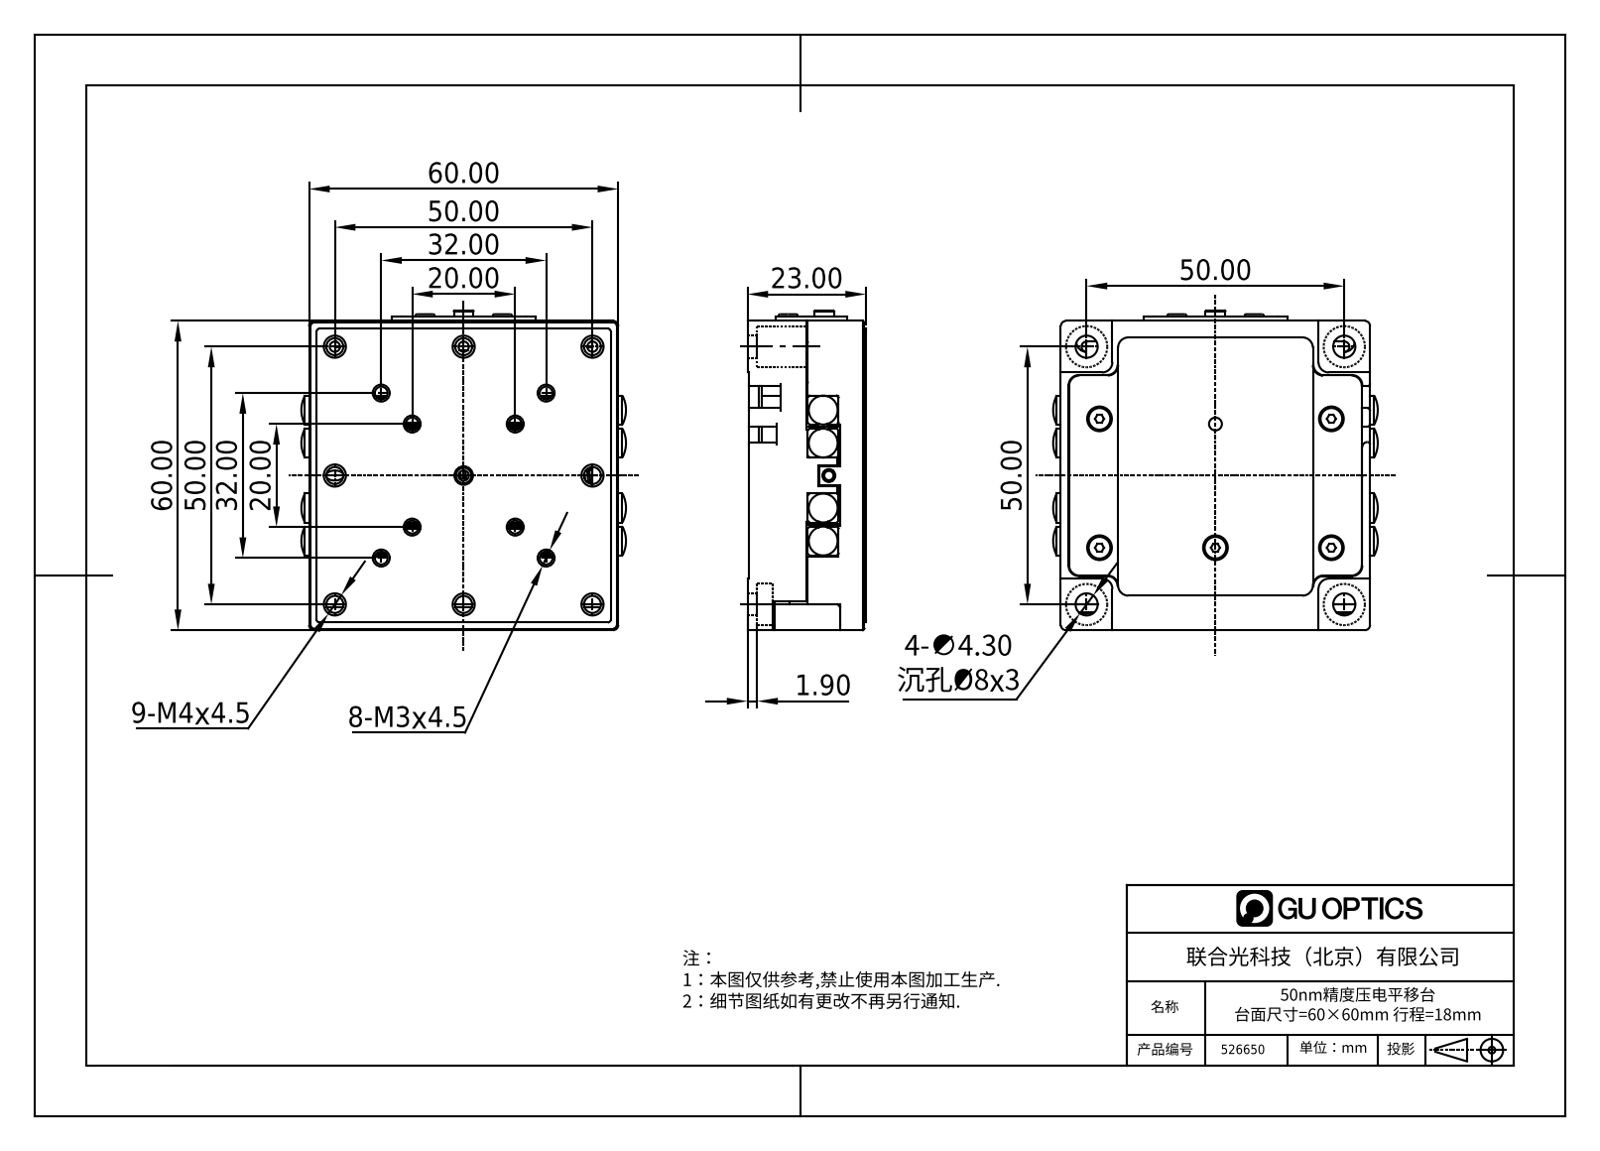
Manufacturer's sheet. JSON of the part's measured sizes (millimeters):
{"part_name": "526650", "step_written_by": "SolidWorks 2020 (CONFIG_CONTROL_DESIGN)", "units": "millimeters", "bodies": {"solids": 0, "faces": 2673, "planar": 1734, "cylindrical": 471, "other": 468}, "overall_size": [63, 62, 23], "round_holes": [[2.5, 25], [2.55, 19], [1.6, 16], [4.4, 16], [1.2, 12], [3.2, 11], [1.5, 8], [3.3, 8], [6, 7], [2.2, 5], [4.2, 5], [4.8, 5]], "round_bosses_or_shafts": [[2, 32], [3, 12], [5.5, 11], [3.8, 11], [5.6, 4], [2.82, 3], [2.2, 3], [3.6, 2]], "partial_cylinders_radius": [[2, 51], [0.2, 20], [1, 16], [0.5, 14], [1.5, 11], [0.8, 10], [1.1, 7], [0.55, 6]], "face_to_face_distances": [11.4, 6.3, 22.7, 11.3, 5, 60, 11.1, 11.6, 17.7, 8.9], "hole_center_spacings": [15, 16.55, 24.21, 30, 25, 7, 19, 30.02]}
